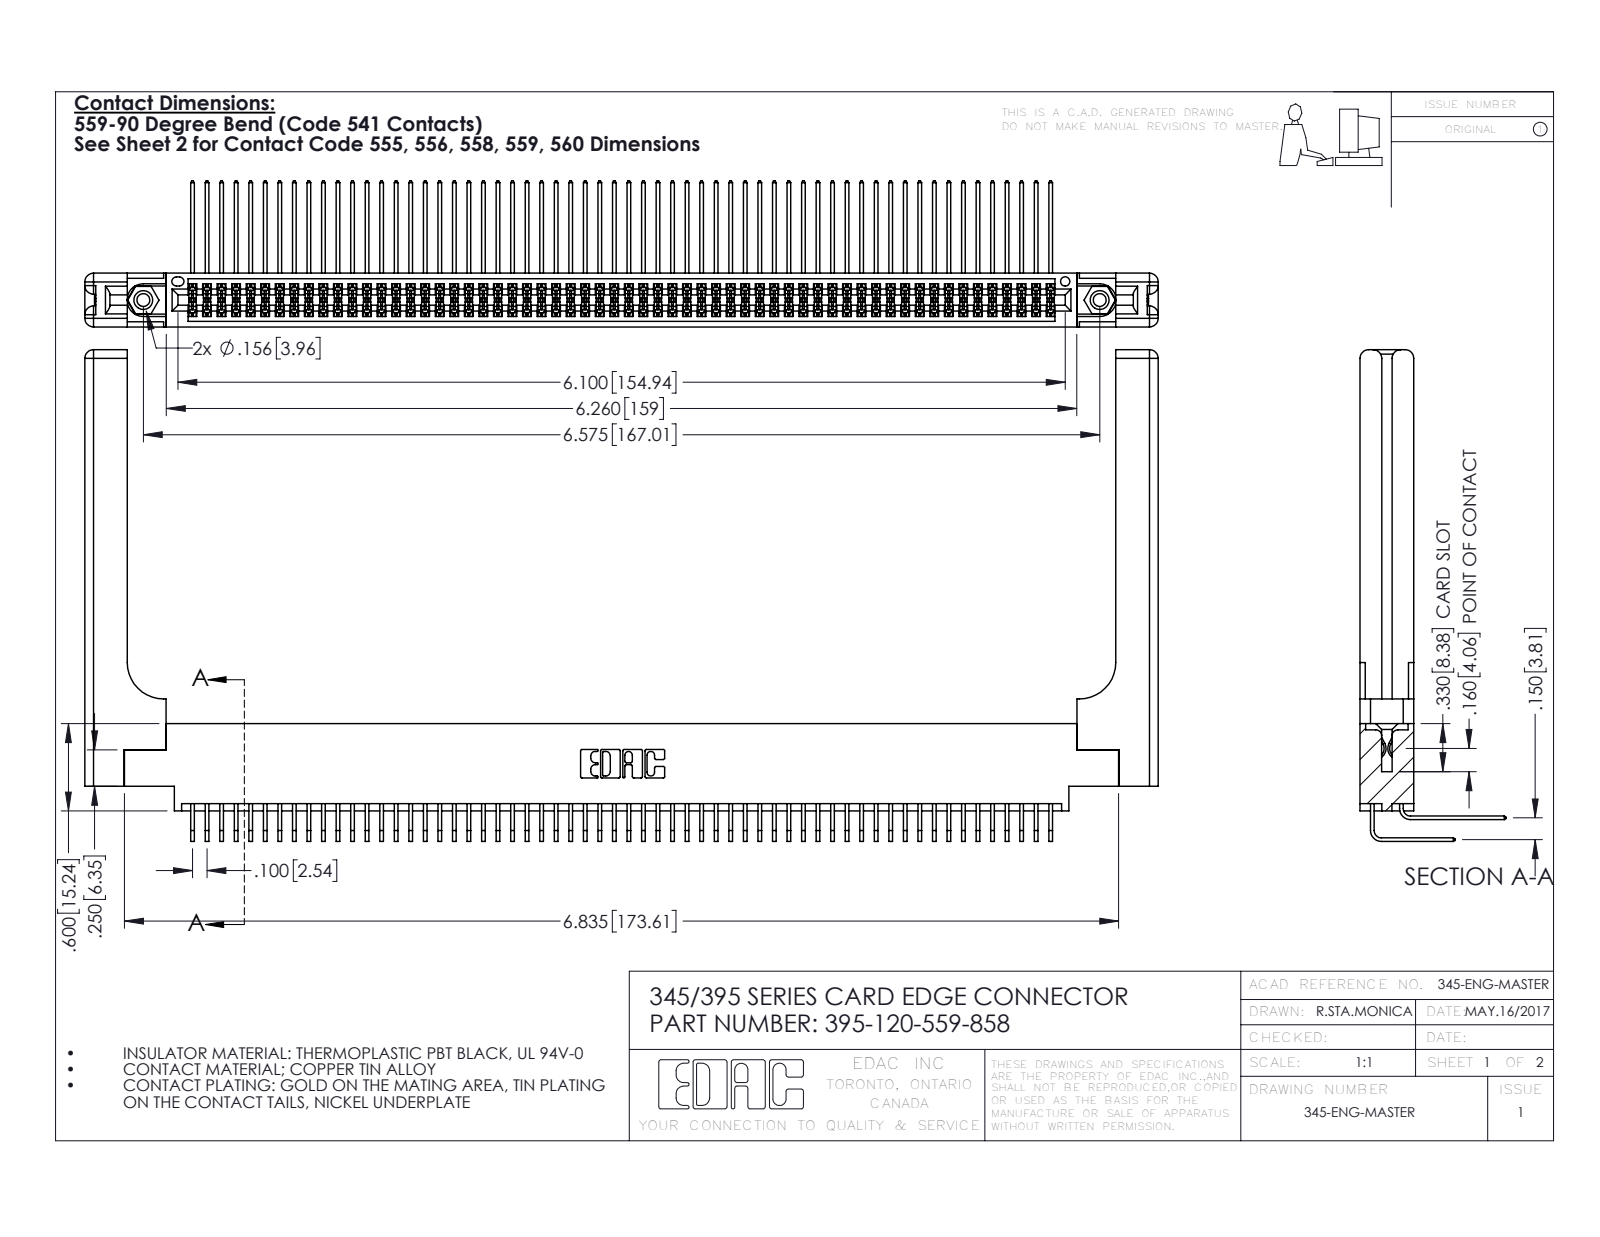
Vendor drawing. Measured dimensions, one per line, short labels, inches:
name: 345-220-058_345-220-058; 345-250-001_345-250-001-102; 345-292-001_559 Tail - 2; 345 Part_0.170 Offset - 0.156 Dia-TH (+2 more)
written by: SolidWorks 2016 (CONFIG_CONTROL_DESIGN)
unit: in
bodies: 125 solids, 6626 faces (4432 planar, 2134 cylindrical, 60 other)
size: 7.379 × 3.379 × 1.005
volume: 1.674 in³; area: 57.07 in²
holes: 2× ⌀0.089, 2× ⌀0.125, 2× ⌀0.156, 1× ⌀0.064
bosses: 2× ⌀0.155
rounds: 181× R0.006, 22× R0.01, 16× R0.06, 6× R0.007, 6× R0.031, 3× R0.026, 2× R0.014, 2× R0.019
face distances: 0.072, 0.298, 0.37, 0.098, 0.272, 0.025, 0.2, 0.225, 0.175, 0.15
hole spacings: 0.27, 6.339, 6.575
